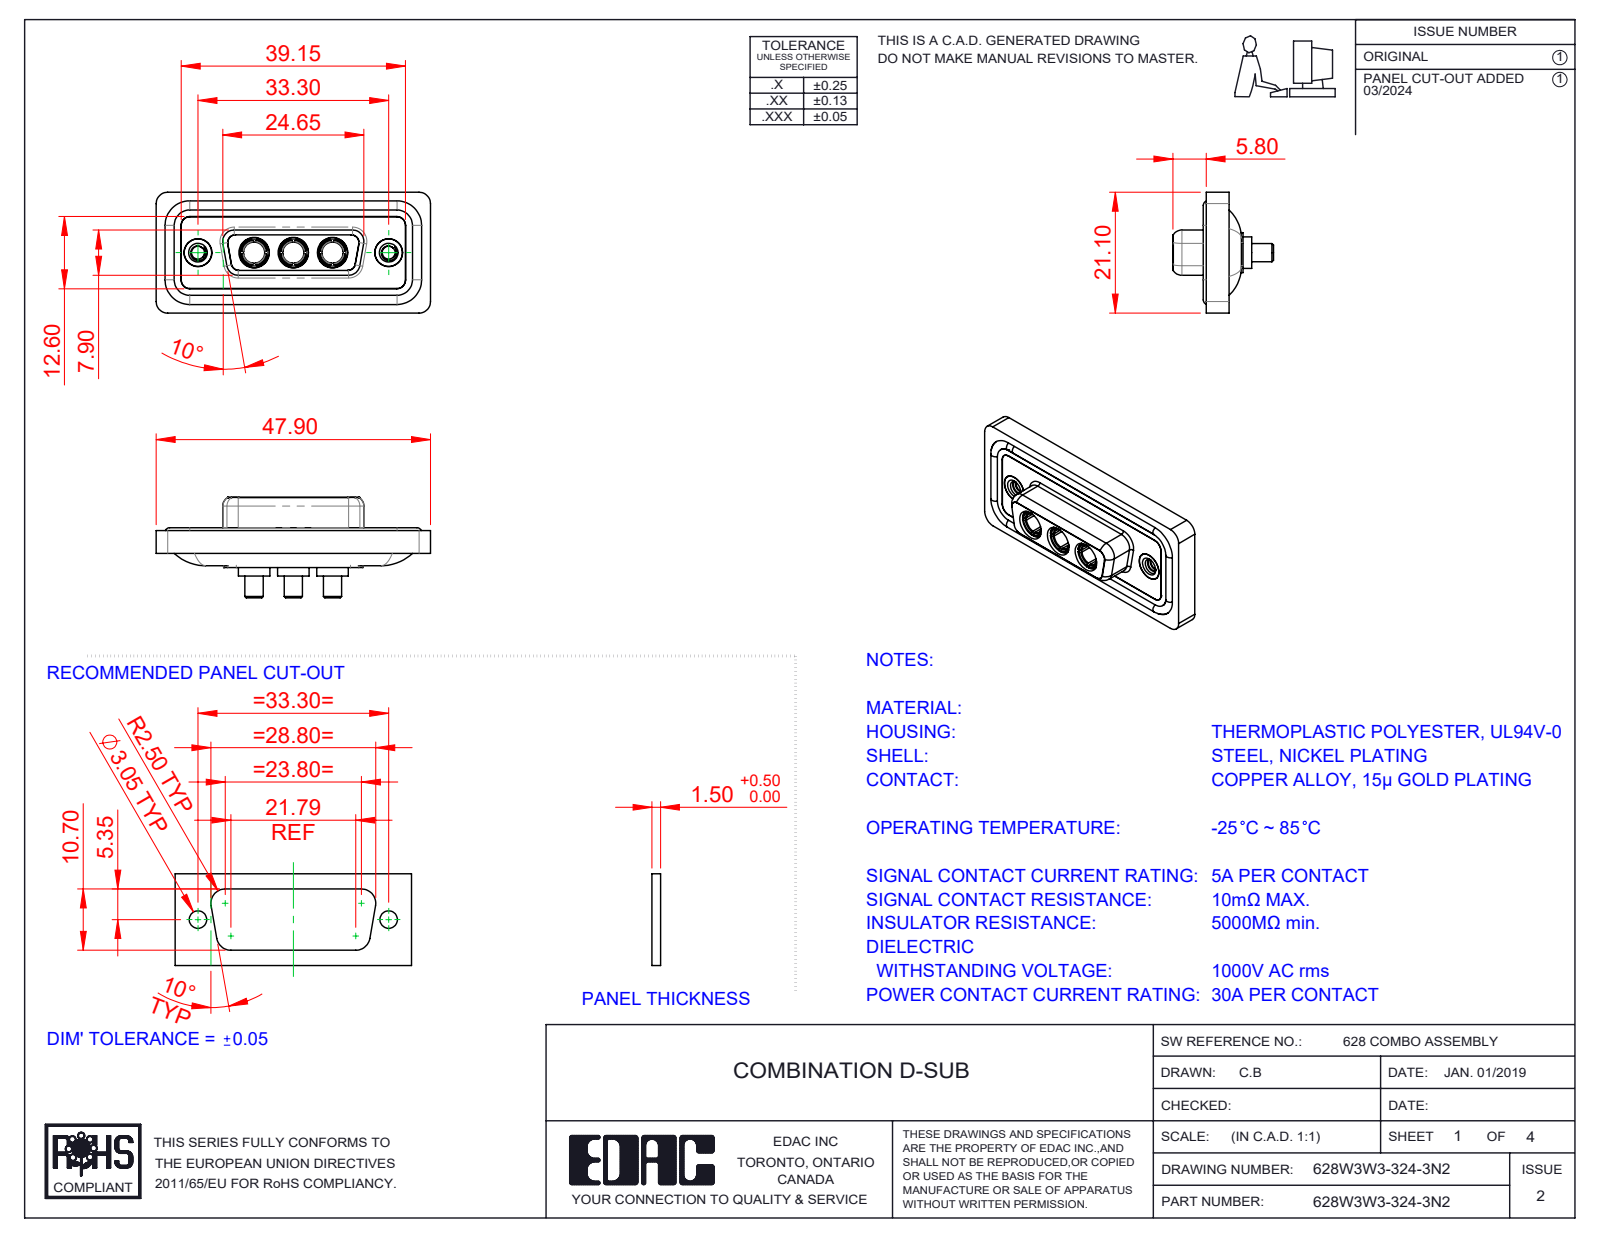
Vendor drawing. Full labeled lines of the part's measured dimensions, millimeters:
Part name (STEP PRODUCT): 628W3W3-324-3N2; 628Combo Housing_3W3; 628Combo Shell Rear_15 Contacts; 628Combo Waterproof Housing_15 Contacts (+3 more)
STEP written by: SolidWorks 2023 (CONFIG_CONTROL_DESIGN)
Units: millimetres
Bodies: 13 solids, 608 faces (192 planar, 257 cylindrical, 159 other)
Overall size (bounding box): 47.9 × 21.1 × 17.55
Volume: 6 048 mm³ · Surface area: 9 752 mm²
Round holes (diameter × count): ⌀4.85 ×5, ⌀3.7 ×3, ⌀5.3 ×3, ⌀2.26 ×2, ⌀4 ×2, ⌀4.05 ×2, ⌀5 ×2
Round bosses / shafts (diameter × count): ⌀1.6 ×4, ⌀5.5 ×3, ⌀5.2 ×3, ⌀4.96 ×3, ⌀4.75 ×3, ⌀3.75 ×3, ⌀3.2 ×3, ⌀4.95 ×2
Partial cylindrical surfaces — rounded edges, fillets, slot ends (radius × count): R1.5 ×22, R2 ×20, R1.35 ×12, R1.6 ×8, R0.25 ×4, R0.5 ×4, R0.6 ×4, R0.65 ×4
Main face-to-face distances: 0.4, 1.8, 1.6, 0.5, 7.45, 1.1, 2.9, 5.65, 7.05, 6.6
Hole centre spacings: 6.85, 9.8, 16.65, 23.5, 13.7, 33.3
